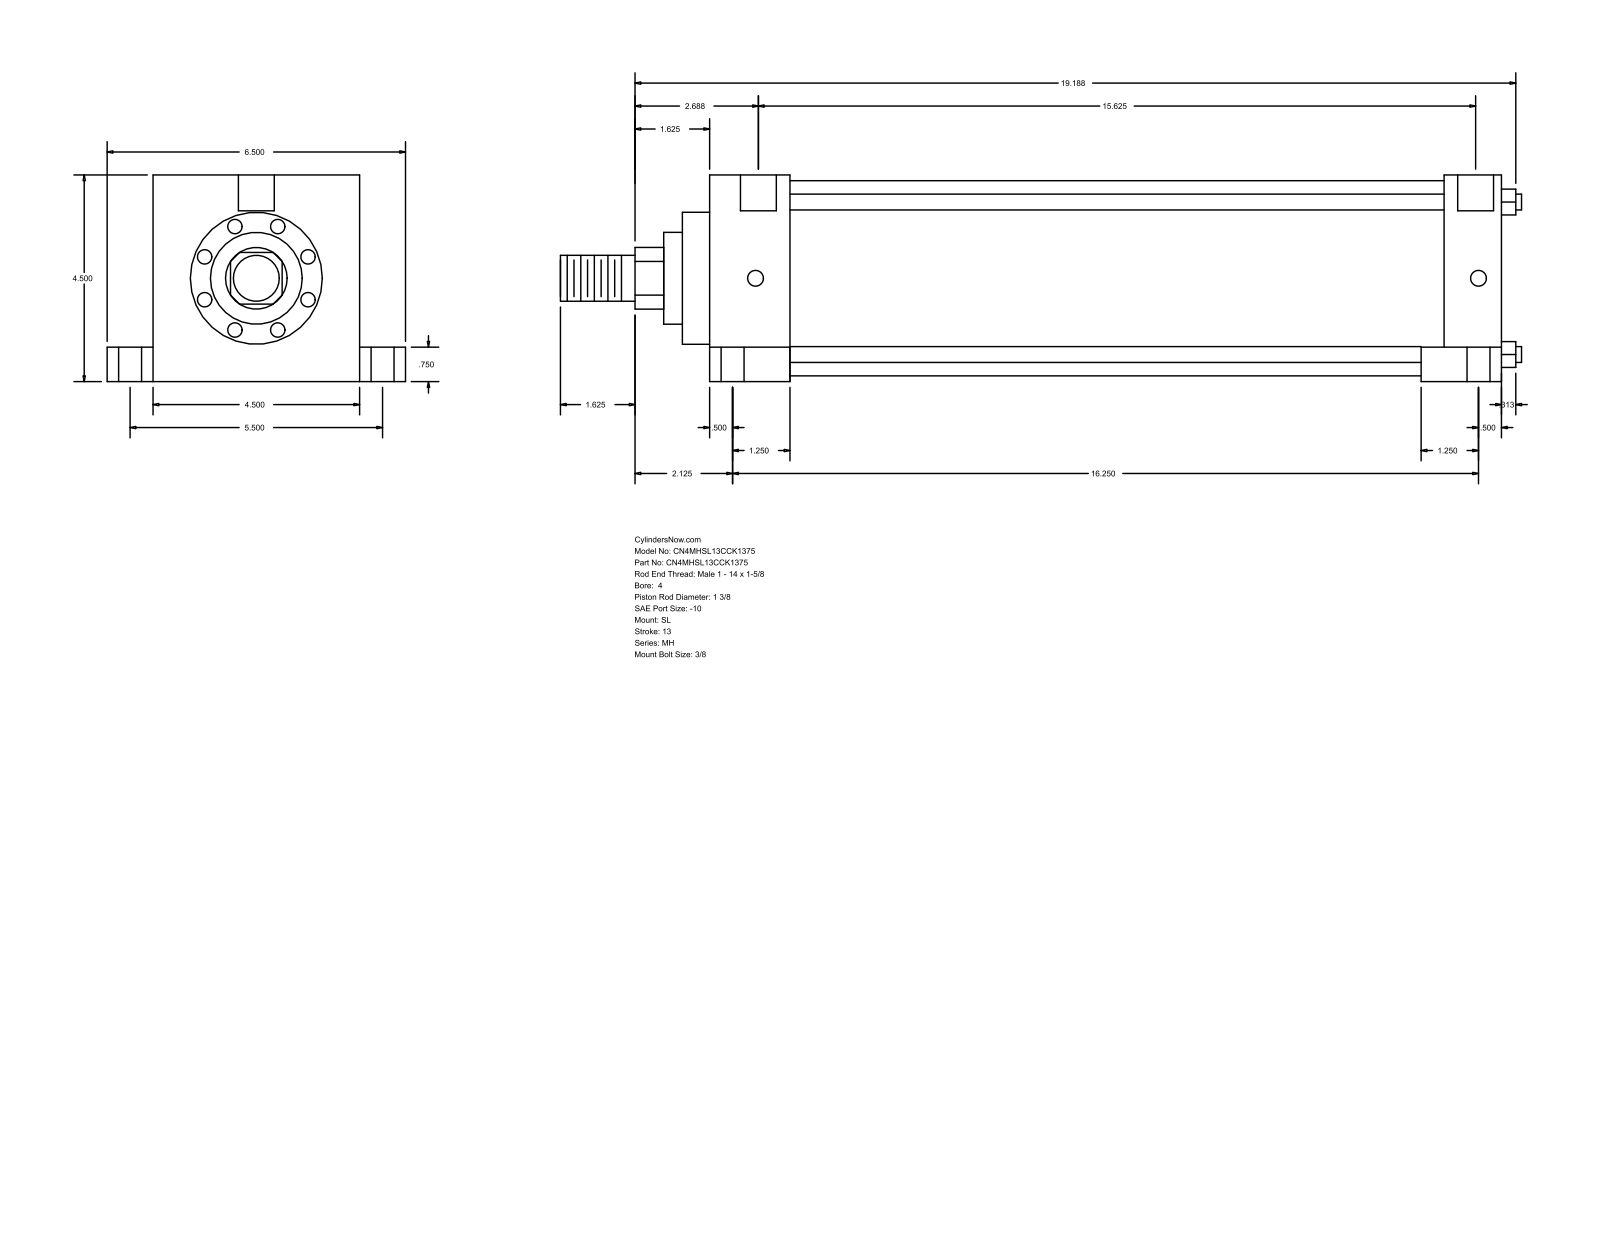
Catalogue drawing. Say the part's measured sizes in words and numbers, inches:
The part is named "MH_SL__0400_1.375". Its 3-D file was written by "GSSL Pune (CONFIG_CONTROL_DESIGN)". It is 0 solids with 110 faces: 77 planar, 33 cylindrical and 0 other. Overall it measures 20.937 by 6.5 by 4.5 inches. Round holes: 4 of diameter 0.344, 4 of diameter 0.5, 4 of diameter 0.75, 2 of diameter 0.781. Round bosses or shafts: 4 of diameter 0.345, 1 of diameter 4.25, 1 of diameter 2.875, 1 of diameter 2, 1 of diameter 1.375, 1 of diameter 1. Partial cylindrical surfaces (rounded edges, fillets, slot ends): 1 of radius 0.672. The main face-to-face distances are 4.5, 17.25, 1.75, 15.5, 16, 14.25, 1.25, 1, 5.5, 0.75. The hole center spacings are 0.063, 2.75, 2.751, 2.795, 2.807, 5.5, 15.688, 15.75.
